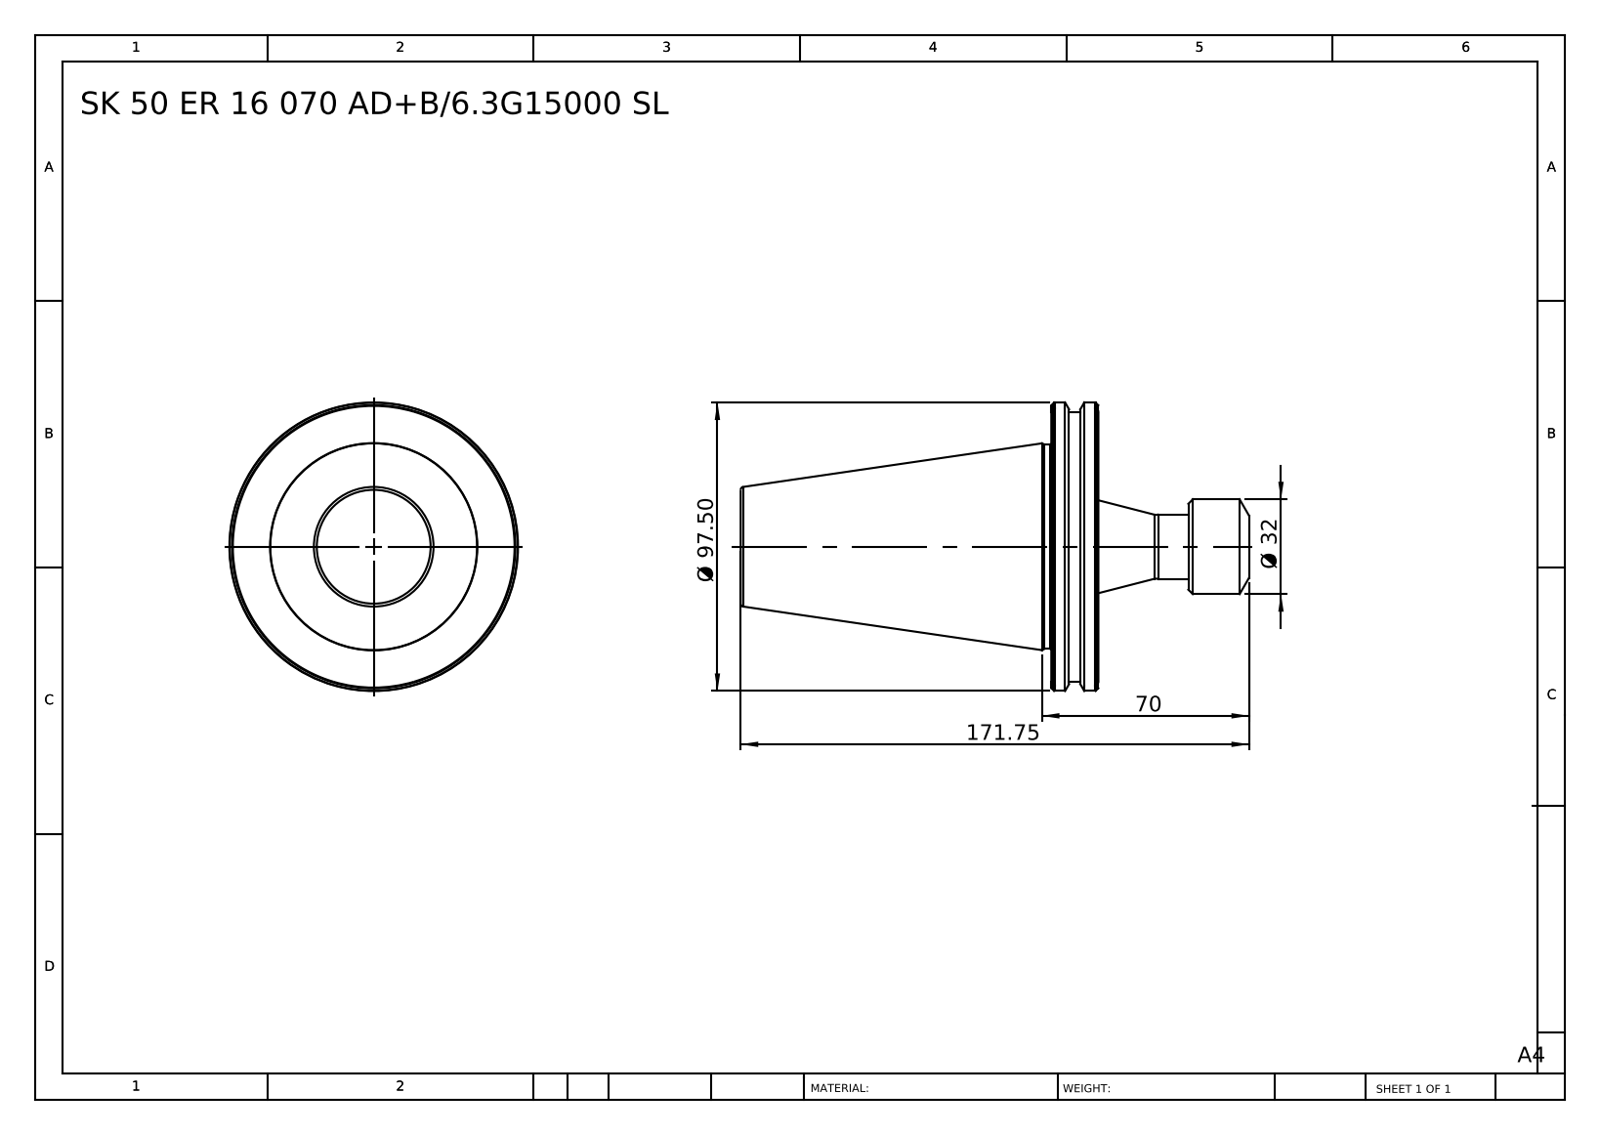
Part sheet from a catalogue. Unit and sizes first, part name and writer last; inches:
Units: inches
Overall size (bounding box): 6.762 × 3.839 × 3.839
Round bosses / shafts (diameter × count): ⌀3.839 ×1, ⌀3.583 ×1, ⌀2.717 ×1, ⌀1.26 ×1, ⌀0.862 ×1
Main face-to-face distances: 0.626, 4.758, 4.132, 2.004, 2.63, 6.762, 0.807, 1.197, 1.823, 5.955
Volume: 24.65 in³ · Surface area: 63.84 in²
Bodies: 1 solid, 71 faces (7 planar, 12 cylindrical, 52 other)
Part name (STEP PRODUCT): SK 50 ER 16 070 AD-6.3G15000 SL
STEP written by: SolidWorks 2014 (CONFIG_CONTROL_DESIGN)
